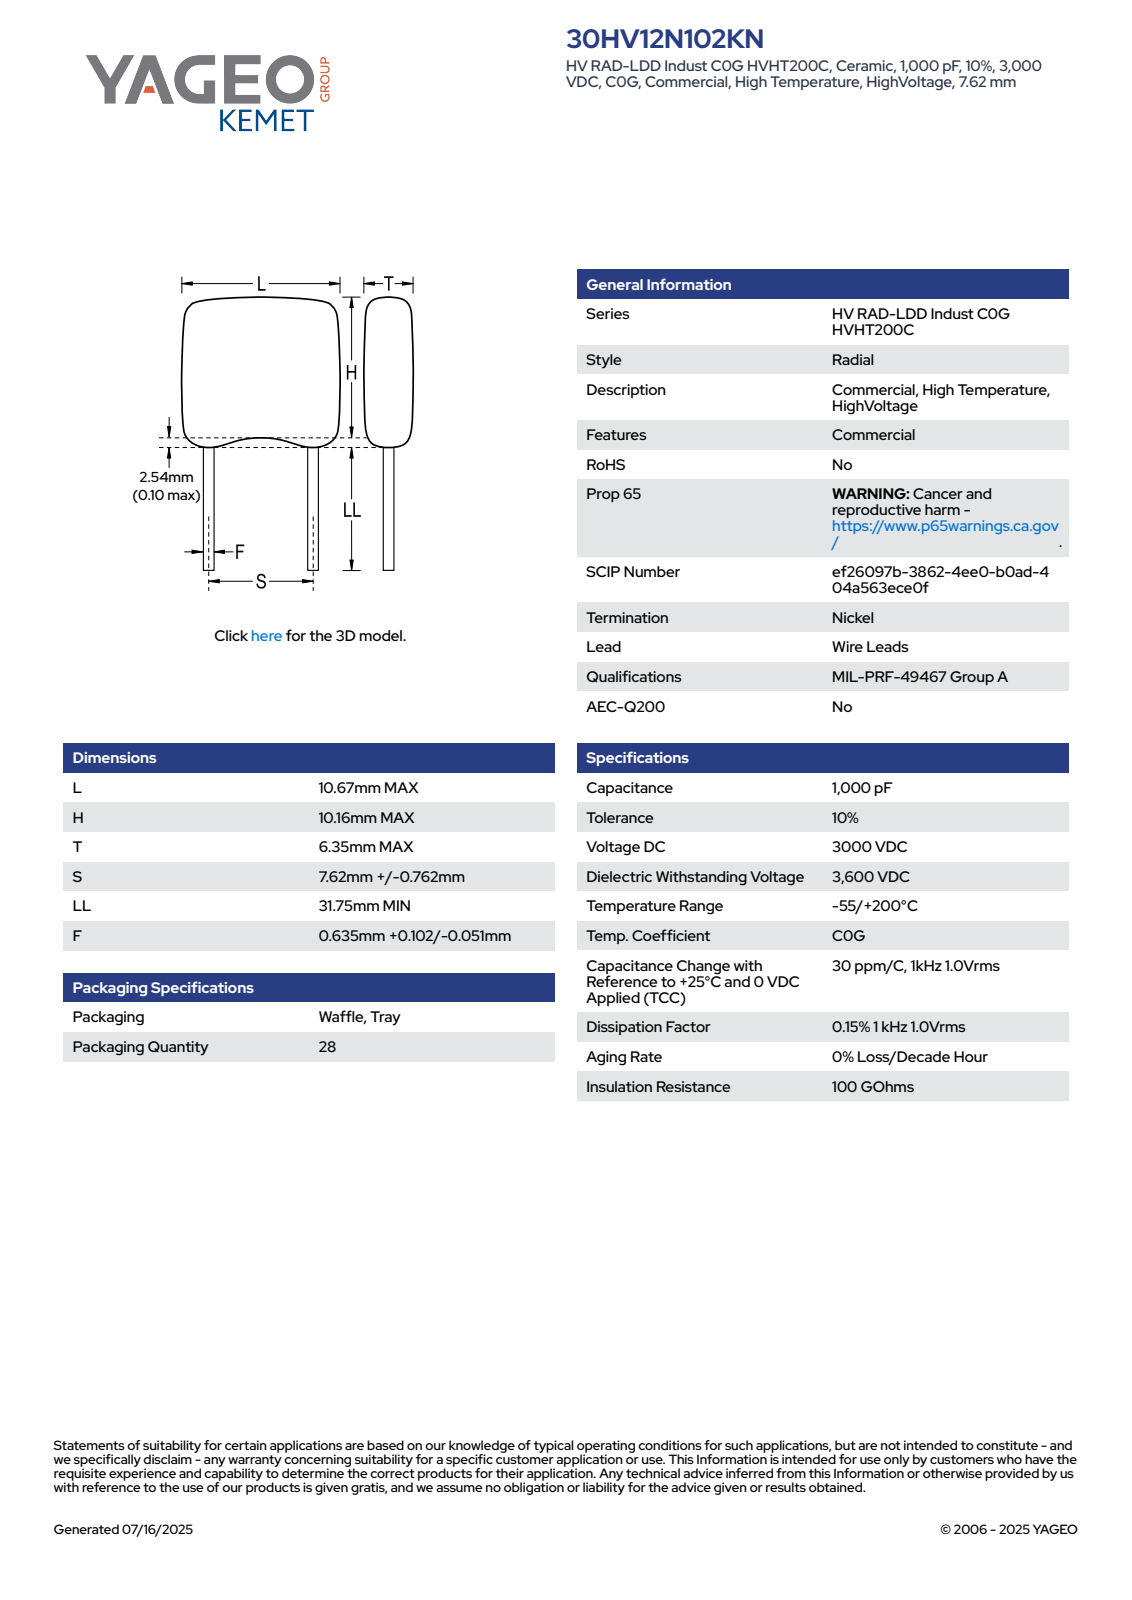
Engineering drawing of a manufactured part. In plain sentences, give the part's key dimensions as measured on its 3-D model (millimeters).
The part is named "CCRM_RCST_HV12_L10.67H10.16T6.35S7.62LL31.75F0.737". Its 3-D file was written by "SolidWorks 2021 (AUTOMOTIVE_DESIGN)". It is 4 solids with 94 faces: 66 planar, 18 cylindrical and 10 other. Overall it measures 14.91 by 10.67 by 6.36 millimeters. Its volume is 722 cubic millimeters and its surface area 509 square millimeters. Round bosses or shafts: 2 of diameter 0.74. Partial cylindrical surfaces (rounded edges, fillets, slot ends): 8 of radius 1, 4 of radius 0.5. The main face-to-face distances are 6.35, 10.67, 11.74, 3.17, 14.91, 5.18, 9.73, 6.56, 8.37, 5.2.
